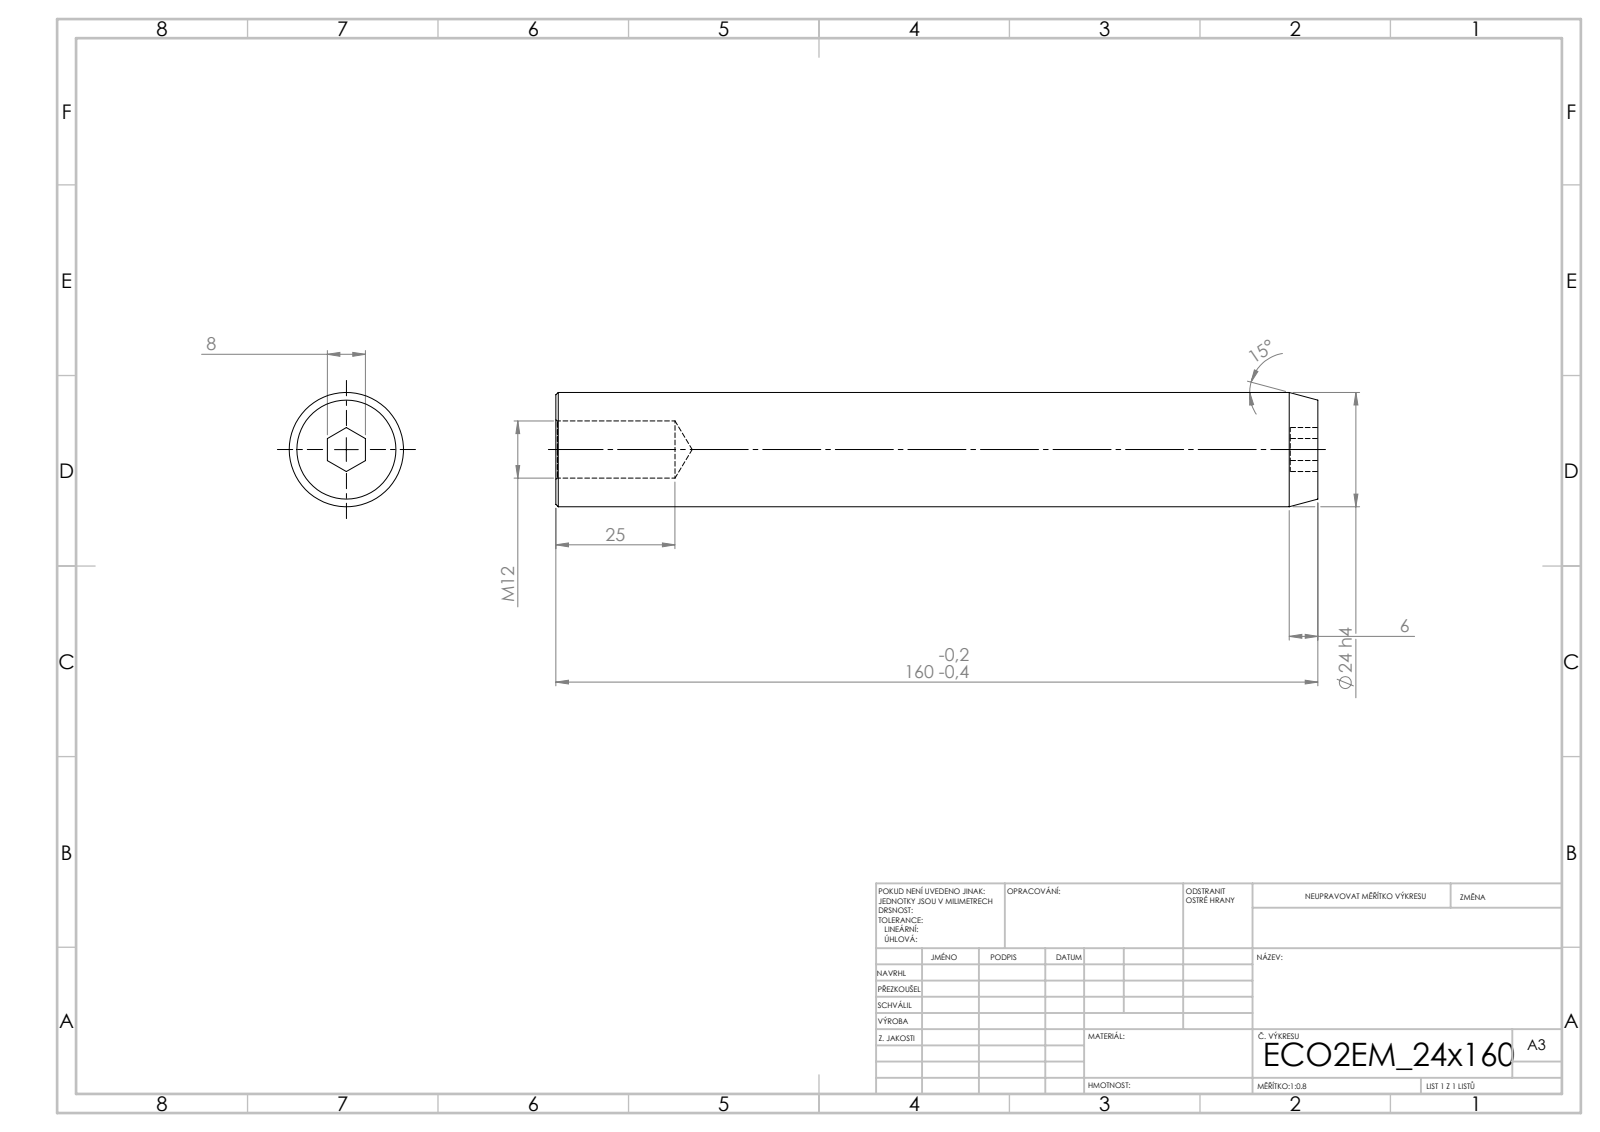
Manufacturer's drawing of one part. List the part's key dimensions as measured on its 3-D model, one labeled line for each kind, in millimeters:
STEP written by: SolidWorks 2019 (CONFIG_CONTROL_DESIGN)
Units: millimetres
Bodies: 1 solid, 21 faces (9 planar, 4 cylindrical, 8 other)
Overall size (bounding box): 160 × 24 × 24
Volume: 68 740 mm³ · Surface area: 13 935 mm²
Round holes (diameter × count): ⌀12 ×1
Round bosses / shafts (diameter × count): ⌀24 ×1
Main face-to-face distances: 160, 8, 5.8, 154.2
